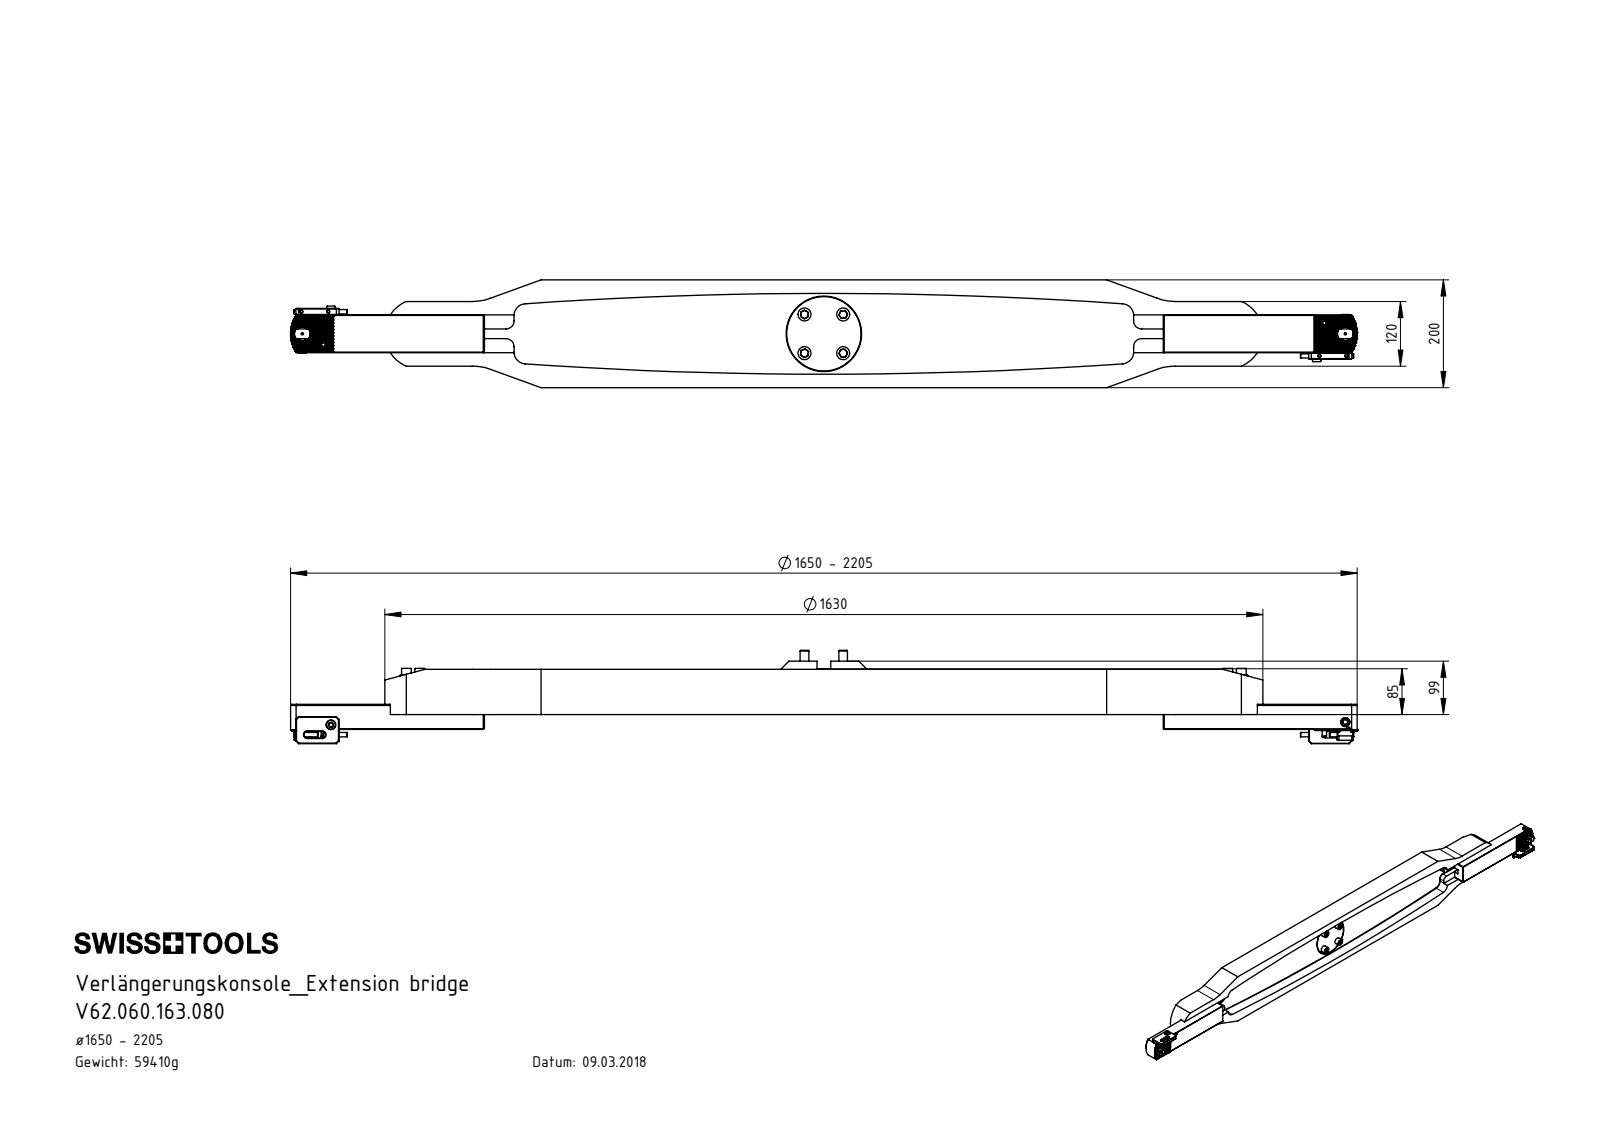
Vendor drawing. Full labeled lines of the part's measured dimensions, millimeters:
Part name (STEP PRODUCT): ISO 4762 - M16 x 80; D60.VK3.163.080; D60-VK3.163.080_A; ISO 4762 - M12 x 80 (+3 more)
STEP written by: SolidWorks 2017 (AUTOMOTIVE_DESIGN)
Units: millimetres
Bodies: 26 solids, 526 faces (278 planar, 147 cylindrical, 101 other)
Overall size (bounding box): 1630 × 200 × 125.5
Volume: 15 080 000 mm³ · Surface area: 1 171 000 mm²
Round holes (diameter × count): ⌀13 ×16, ⌀18 ×12, ⌀12 ×4, ⌀17 ×4, ⌀60 ×1, ⌀140 ×1
Round bosses / shafts (diameter × count): ⌀24 ×12, ⌀18 ×4, ⌀16 ×4, ⌀12 ×4, ⌀138 ×1
Partial cylindrical surfaces — rounded edges, fillets, slot ends (radius × count): R2 ×14, R22 ×12, R8 ×4, R10 ×4, R15 ×4, R100 ×4, R65 ×2, R120 ×1
Main face-to-face distances: 32, 13, 45, 84, 71, 39, 200, 40, 44, 160
Hole centre spacings: 25, 47.17, 40, 50, 64.03, 1475, 1475.54, 1450
